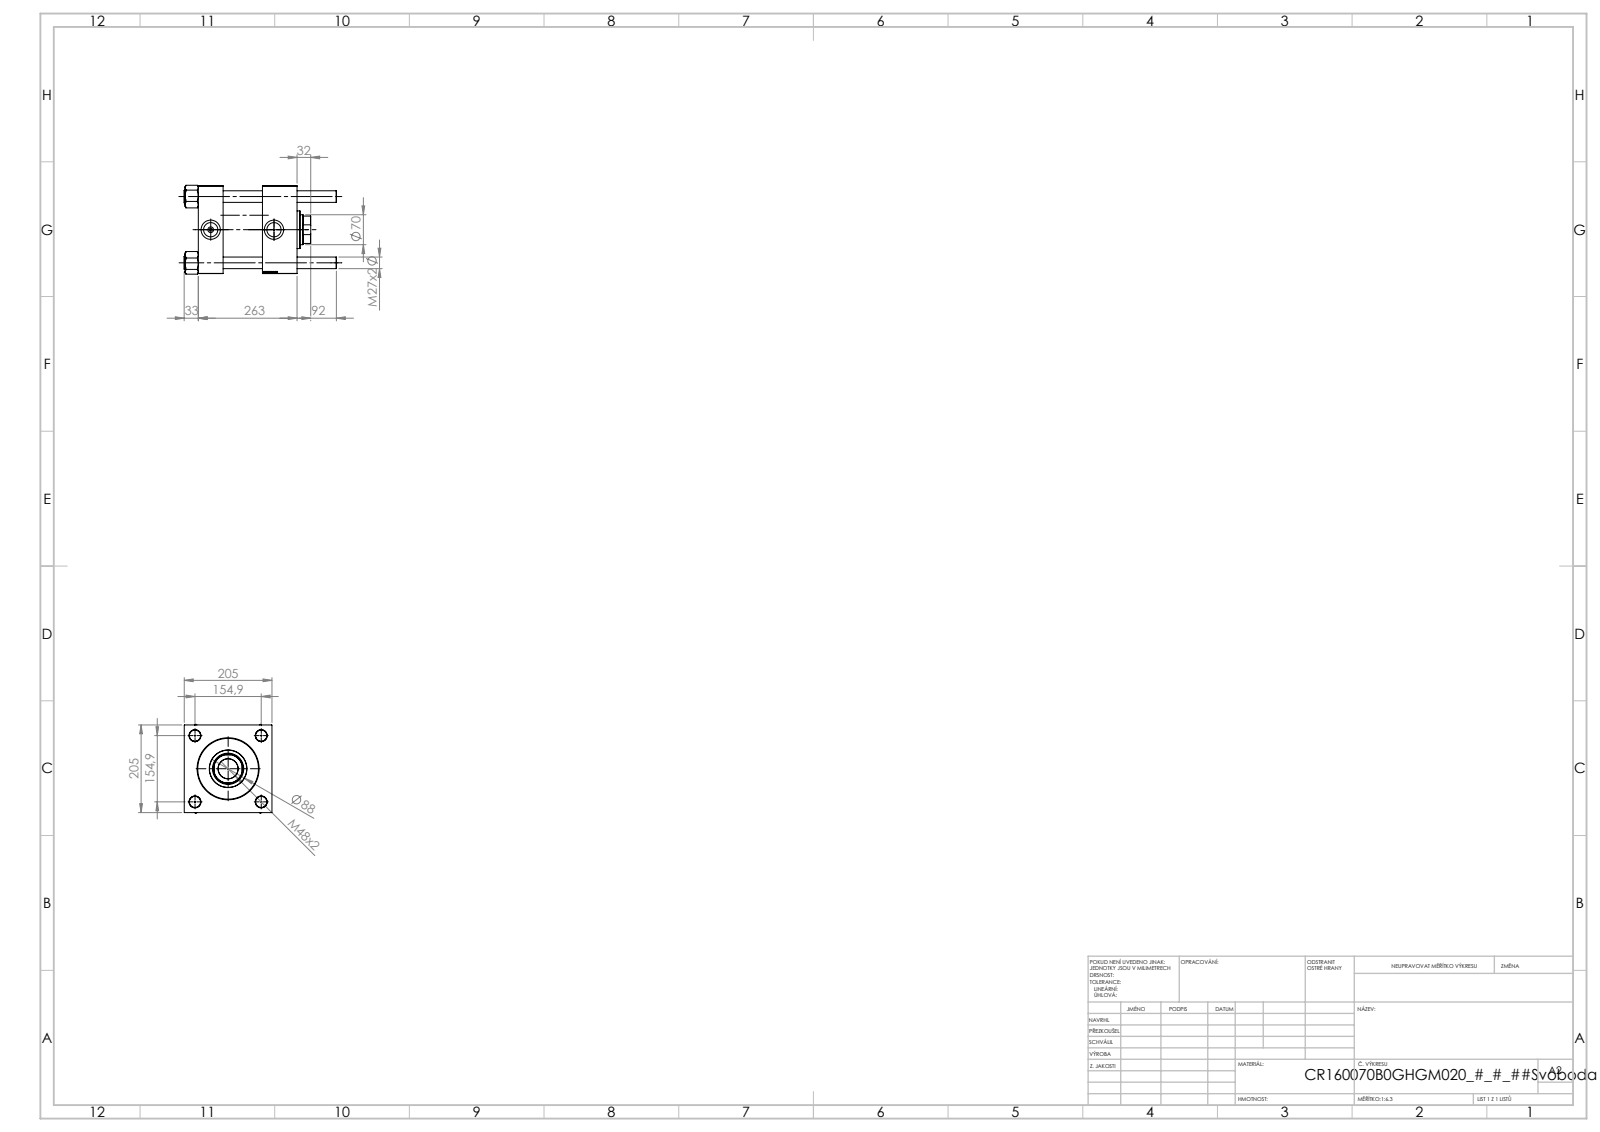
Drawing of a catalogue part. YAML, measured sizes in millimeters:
part_name: "V215_VC_A; V215CR_VCP_B; V215CR_B-1; V215CR_B_TYCINKA (+1 more)"
step_written_by: "SolidWorks 2019 (CONFIG_CONTROL_DESIGN)"
units: millimeters
bodies: {solids: 11, faces: 1206, planar: 480, cylindrical: 78, other: 648}
overall_size: [356, 207.94, 205]
volume: 7753000
surface_area: 753840
round_holes:
  - {diameter: 27, count: 4}
  - {diameter: 7, count: 2}
  - {diameter: 33.24, count: 2}
  - {diameter: 45, count: 2}
  - {diameter: 46.5, count: 1}
  - {diameter: 70, count: 1}
  - {diameter: 73, count: 1}
  - {diameter: 120, count: 1}
  - {diameter: 142, count: 1}
  - {diameter: 160, count: 1}
round_bosses_or_shafts:
  - {diameter: 30, count: 4}
  - {diameter: 166, count: 1}
  - {diameter: 88, count: 1}
partial_cylinders:
  - {radius: 34, count: 1}
face_to_face_distances: [205, 58, 173, 231, 92, 150, 81, 202.3, 144.3, 52.3]
hole_center_spacings: [109.53, 154.9, 219.06, 148]
